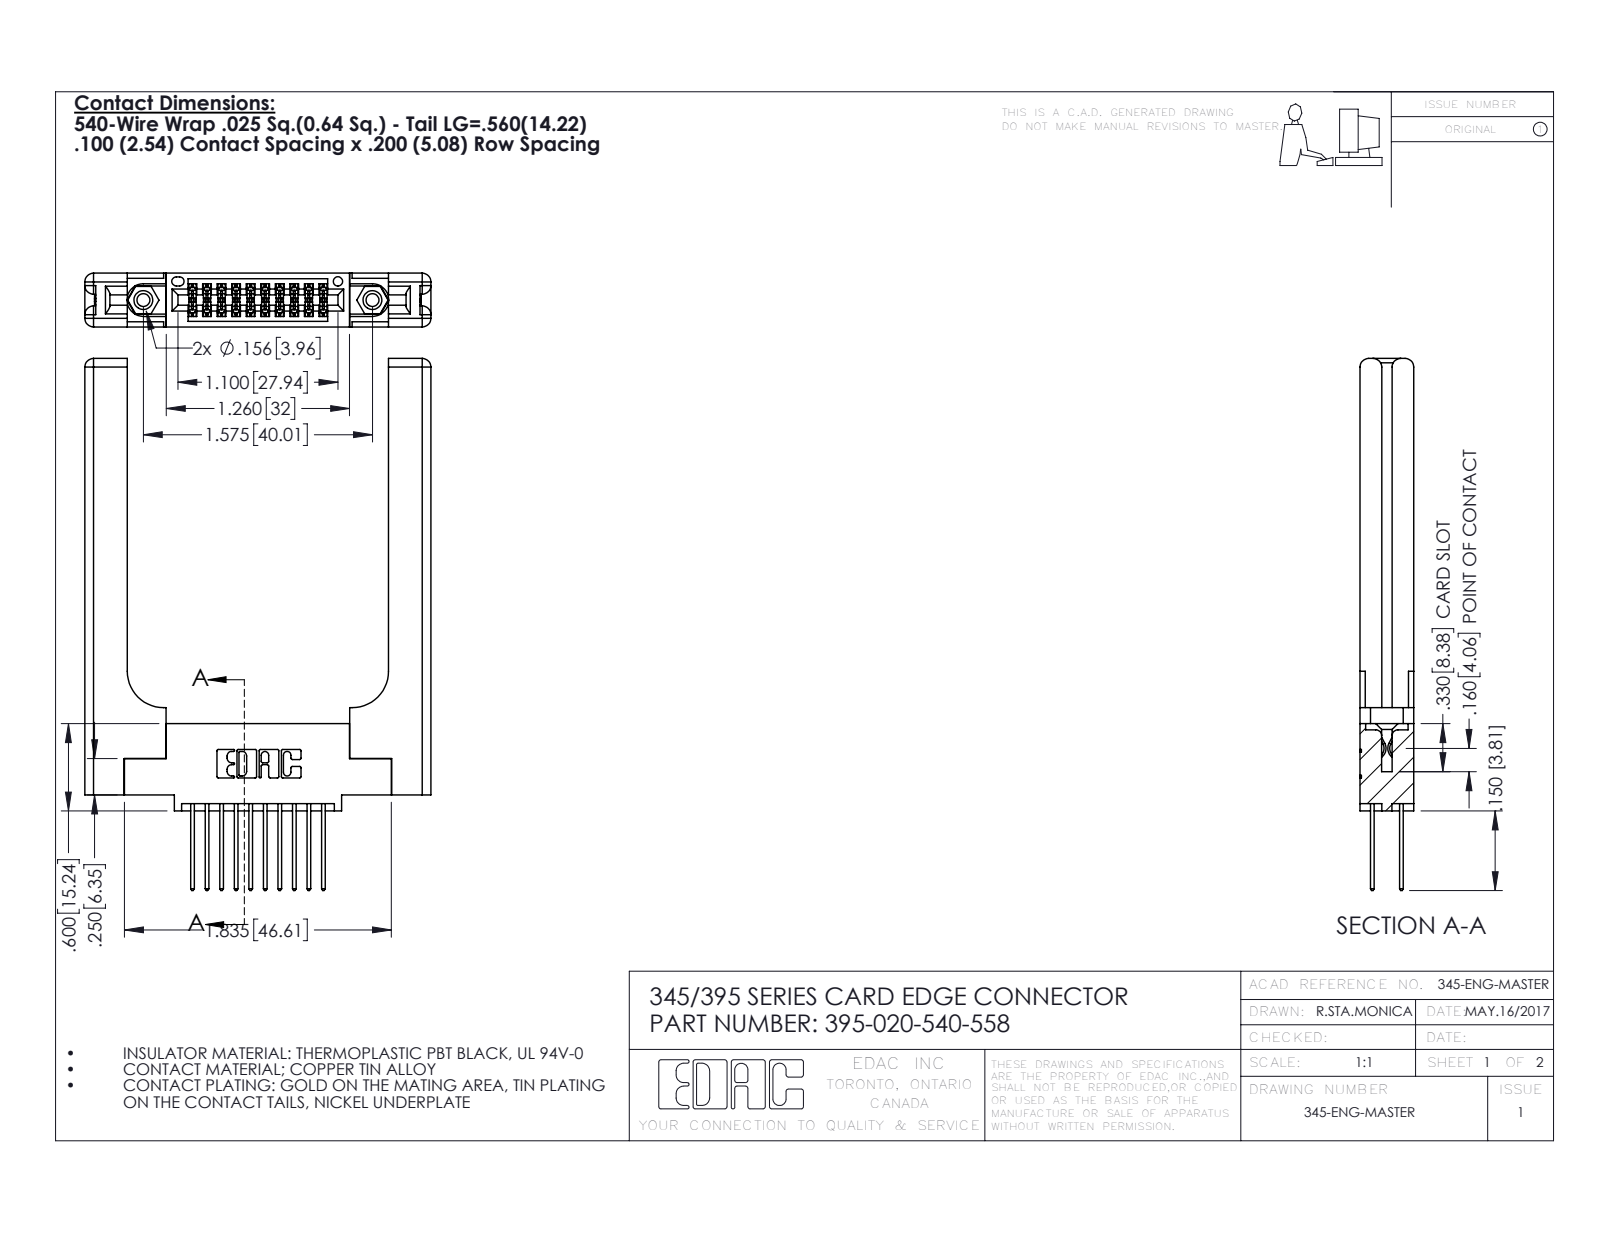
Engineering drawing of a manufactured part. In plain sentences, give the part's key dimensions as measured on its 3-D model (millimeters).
The part is named "345-250-001_345-250-001-102; 345-292-001_345-293-140; 395-020-540-558; 345-220-058_345-220-058 (+1 more)". Its 3-D file was written by "SolidWorks 2016 (CONFIG_CONTROL_DESIGN)". It is 25 solids with 1386 faces: 892 planar, 434 cylindrical and 60 other. Overall it measures 92.9 by 60.4 by 9.4 millimeters. Its volume is 14 000 cubic millimeters and its surface area 13 120 square millimeters. Round holes: 2 of diameter 2.3, 2 of diameter 3.2, 2 of diameter 4, 1 of diameter 1.6. Round bosses or shafts: 2 of diameter 3.9. Partial cylindrical surfaces (rounded edges, fillets, slot ends): 30 of radius 0.2, 22 of radius 0.3, 20 of radius 0.3, 16 of radius 1.5, 6 of radius 0.2, 6 of radius 0.8, 3 of radius 0.7, 2 of radius 0.4. The main face-to-face distances are 9.4, 1.8, 7.6, 3.8, 3.8, 2, 5.6, 5.1, 2.5, 6.9. The hole center spacings are 6.9, 34.1, 40.
